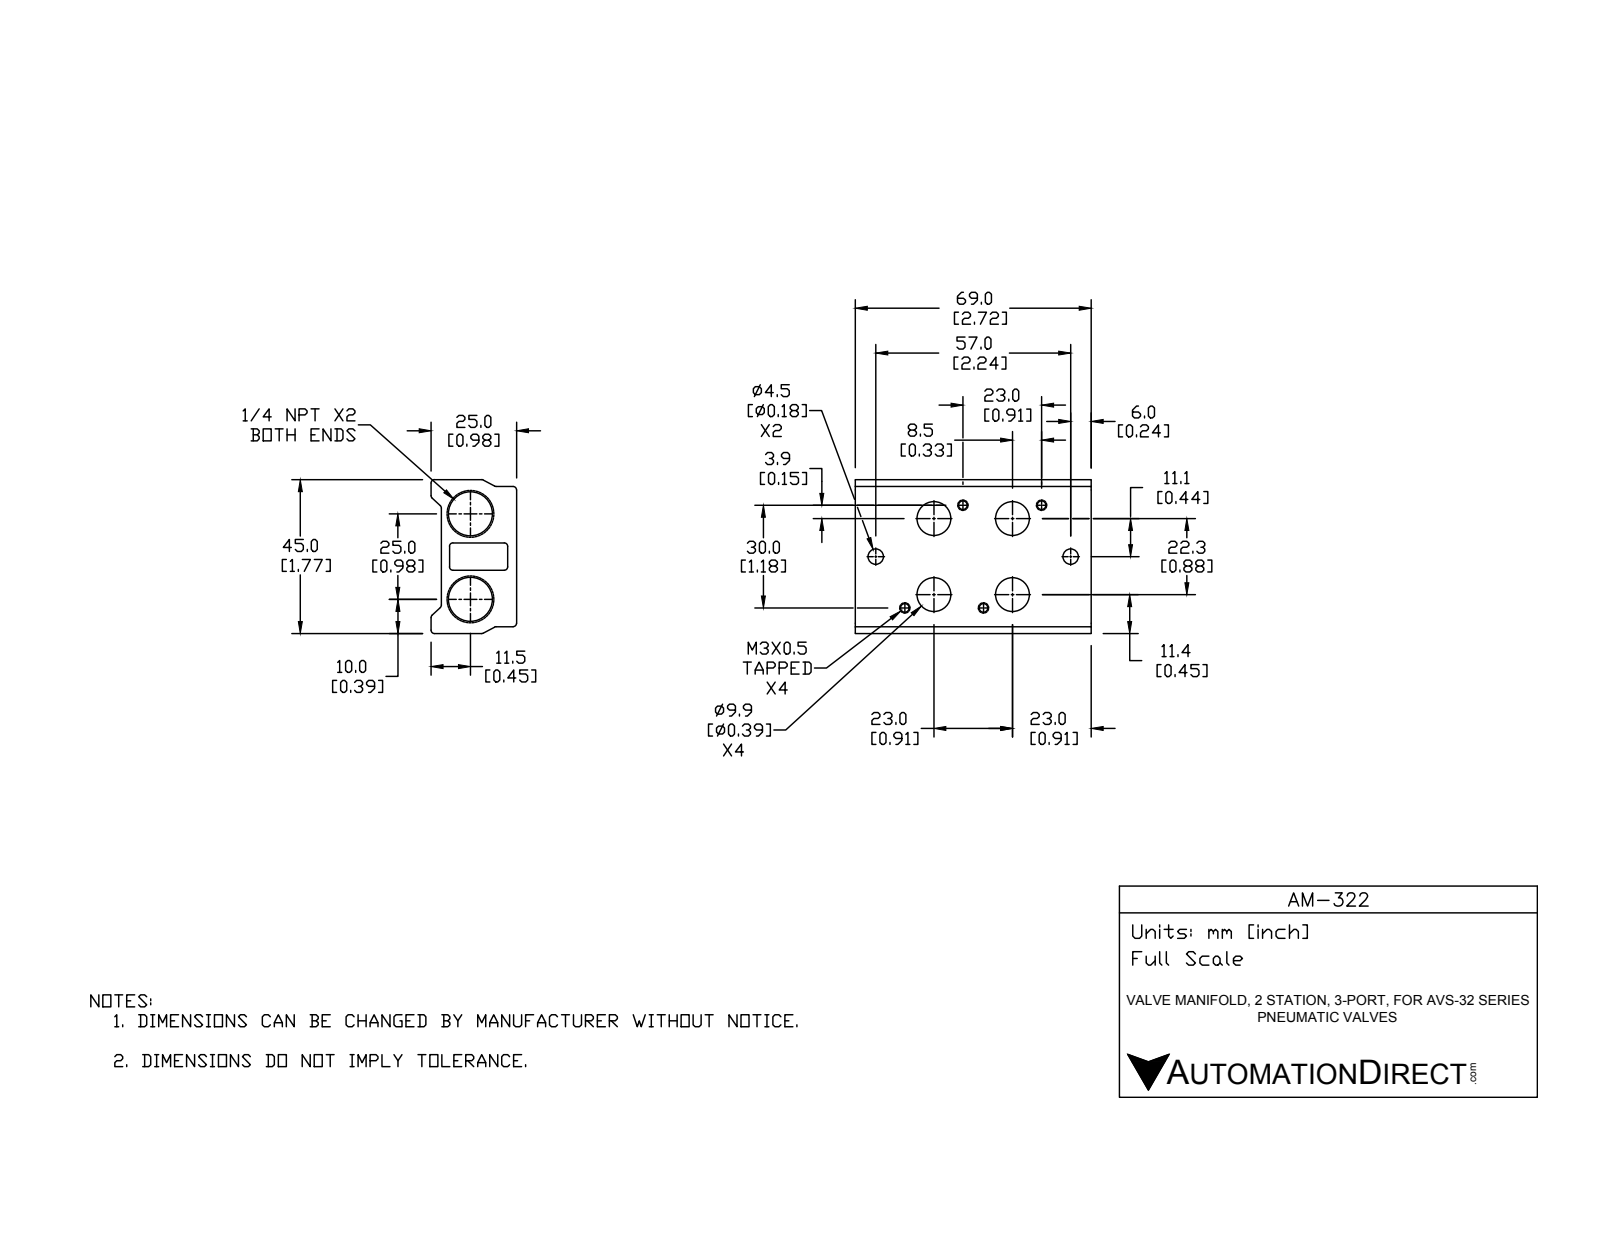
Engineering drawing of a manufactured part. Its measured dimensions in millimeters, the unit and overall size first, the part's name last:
Units: millimetres
Overall size (bounding box): 69 × 45 × 25
Round holes (diameter × count): ⌀2.5 ×4, ⌀9.9 ×4, ⌀4.5 ×2, ⌀11.11 ×2, ⌀11.13 ×2
Partial cylindrical surfaces — rounded edges, fillets, slot ends (radius × count): R1 ×16
Main face-to-face distances: 22, 18.5, 26.5, 8, 45, 2, 43, 16.5, 24.5, 69
Hole centre spacings: 9.34, 20.31, 23, 27.47, 41.52, 15.01, 17.24, 22.24
Volume: 41 281 mm³ · Surface area: 19 948 mm²
Bodies: 1 solid, 100 faces (22 planar, 52 cylindrical, 26 other)
Part name (STEP PRODUCT): AM-322
STEP written by: SolidWorks 2016 (AUTOMOTIVE_DESIGN)
